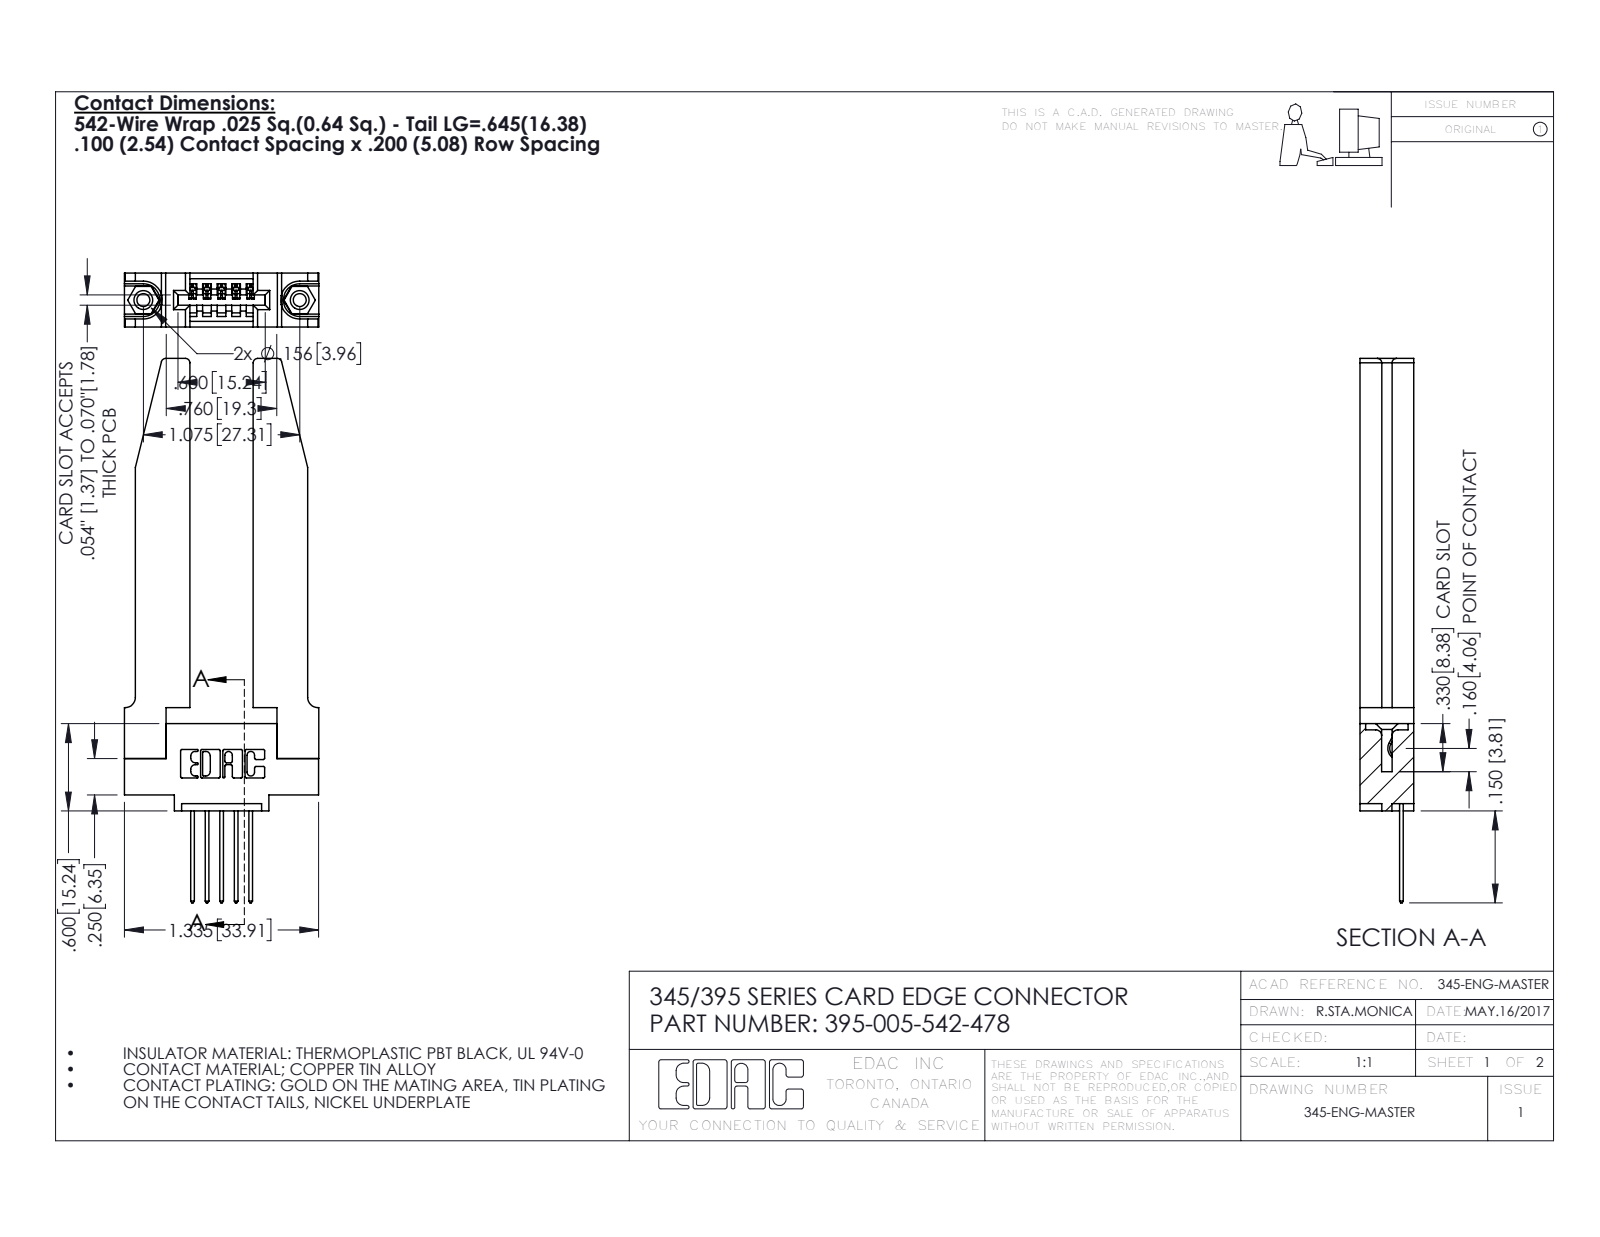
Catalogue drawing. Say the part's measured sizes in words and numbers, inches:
The part is named "345-220-078_345-220-078; 345-292-001_345-293-142; 345 Part_0.110 Offset - 0.156 Dia-TH; 345-250-001_345-250-001-102 (+1 more)". Its 3-D file was written by "SolidWorks 2016 (CONFIG_CONTROL_DESIGN)". It is 10 solids with 654 faces: 426 planar, 176 cylindrical and 52 other. Overall it measures 3.742 by 1.336 by 0.37 inches. Its volume is 0.649 cubic inches and its surface area 15.95 square inches. Round holes: 2 of diameter 0.089, 2 of diameter 0.125, 2 of diameter 0.156, 1 of diameter 0.064. Round bosses or shafts: 2 of diameter 0.155. Partial cylindrical surfaces (rounded edges, fillets, slot ends): 22 of radius 0.01, 10 of radius 0.006, 10 of radius 0.01, 8 of radius 0.03, 6 of radius 0.007, 6 of radius 0.031, 3 of radius 0.026, 2 of radius 0.031. The main face-to-face distances are 0.37, 0.15, 0.22, 0.435, 0.072, 0.148, 0.298, 0.077, 0.2, 0.071. The hole center spacings are 0.27, 0.847, 1.075.
